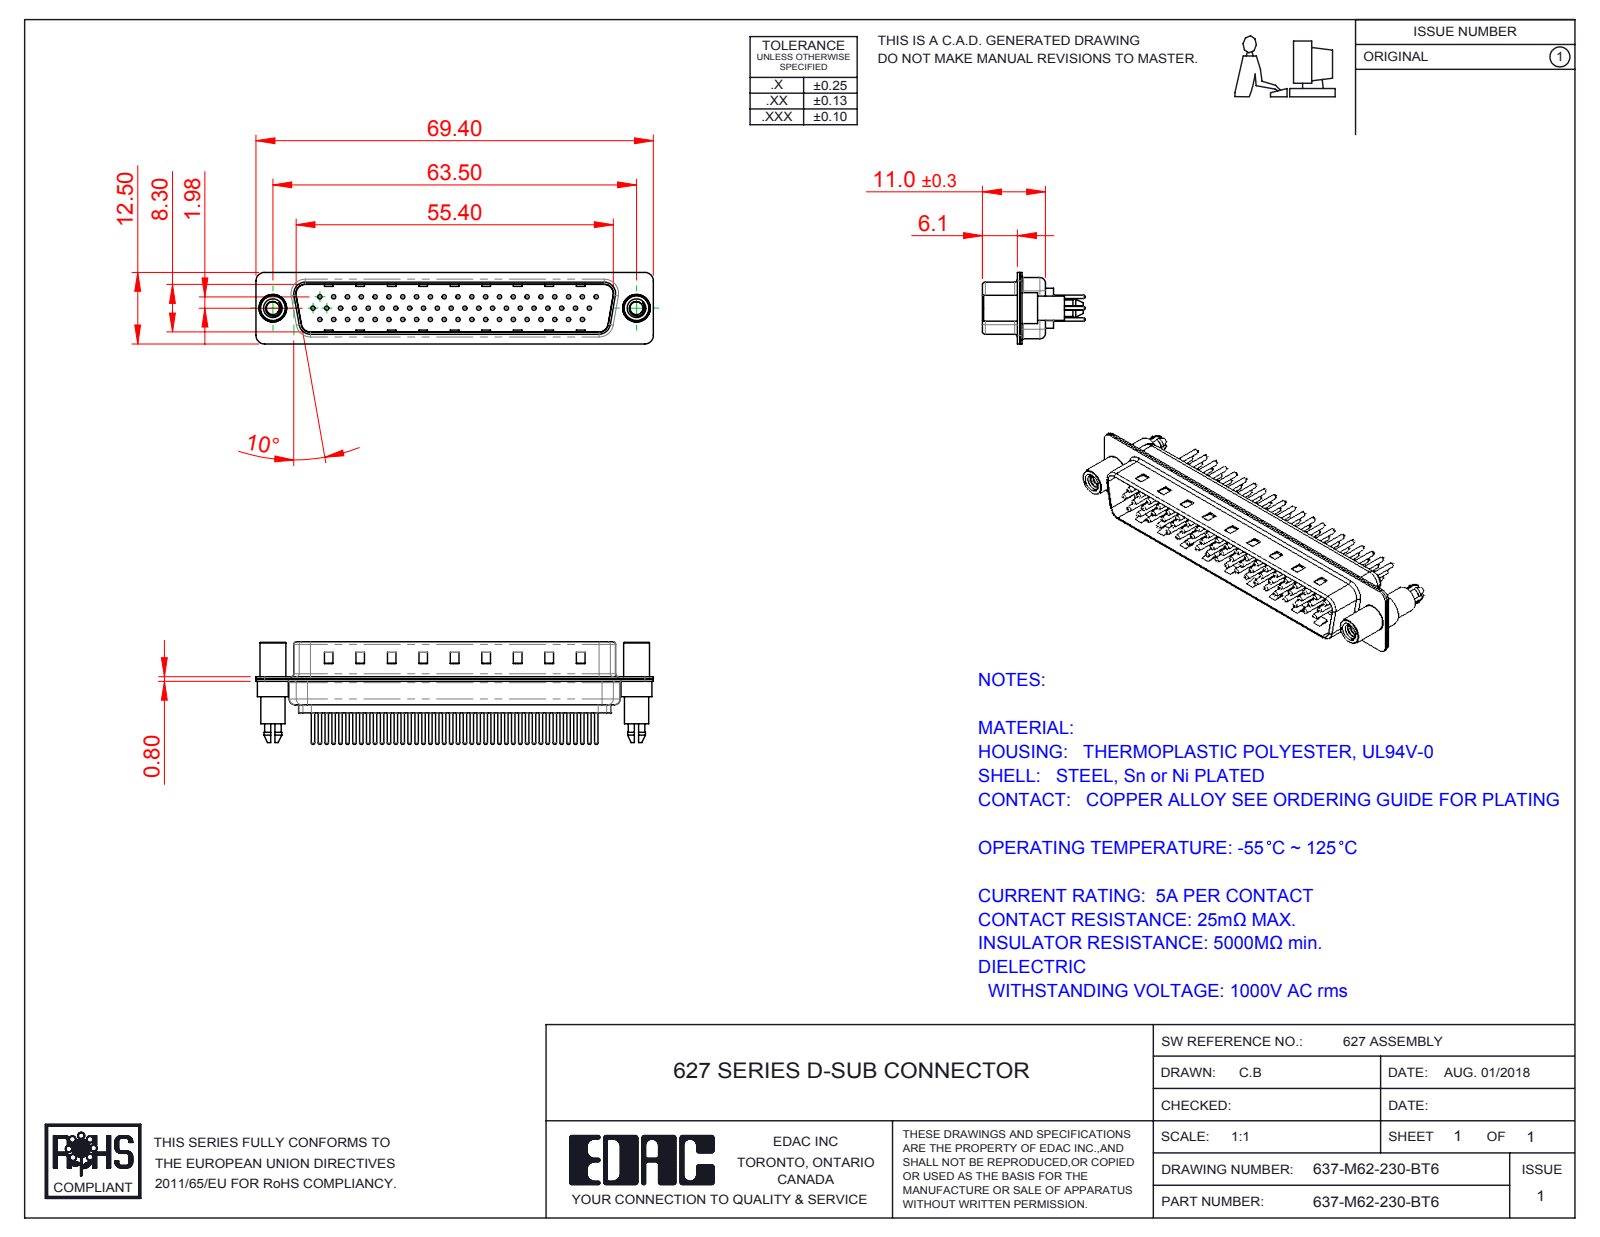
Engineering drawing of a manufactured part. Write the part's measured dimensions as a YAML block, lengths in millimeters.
part_name: "637M Contact Row 1_30; 637M Shell Rear_62 Contacts; 637-M62-230-BT6; 637M Shell Front_62 Contacts (+4 more)"
step_written_by: "SolidWorks 2016 (CONFIG_CONTROL_DESIGN)"
units: millimeters
bodies: {solids: 67, faces: 2790, planar: 675, cylindrical: 1045, other: 1070}
overall_size: [69.4, 17.9, 12.5]
volume: 4254
surface_area: 11898
round_holes:
  - {diameter: 0.75, count: 62}
  - {diameter: 1.6, count: 62}
  - {diameter: 2, count: 62}
  - {diameter: 2.26, count: 2}
  - {diameter: 4, count: 2}
  - {diameter: 4.8, count: 2}
round_bosses_or_shafts:
  - {diameter: 1.5, count: 62}
  - {diameter: 0.6, count: 62}
  - {diameter: 5.4, count: 2}
  - {diameter: 4.9, count: 2}
  - {diameter: 4.5, count: 2}
  - {diameter: 4.25, count: 2}
partial_cylinders:
  - {radius: 1.5, count: 18}
  - {radius: 2, count: 12}
  - {radius: 1.6, count: 10}
  - {radius: 0.5, count: 8}
  - {radius: 0.25, count: 4}
  - {radius: 0.6, count: 4}
  - {radius: 0.65, count: 4}
  - {radius: 0.9, count: 4}
face_to_face_distances: [0.4, 0.8, 9.5, 9.1, 8.7, 9.9, 0.75, 0.35, 5.9, 1.2]
hole_center_spacings: [7.24, 2.32, 2.41, 4.13, 9.65, 4.83, 14.48, 11.04]
